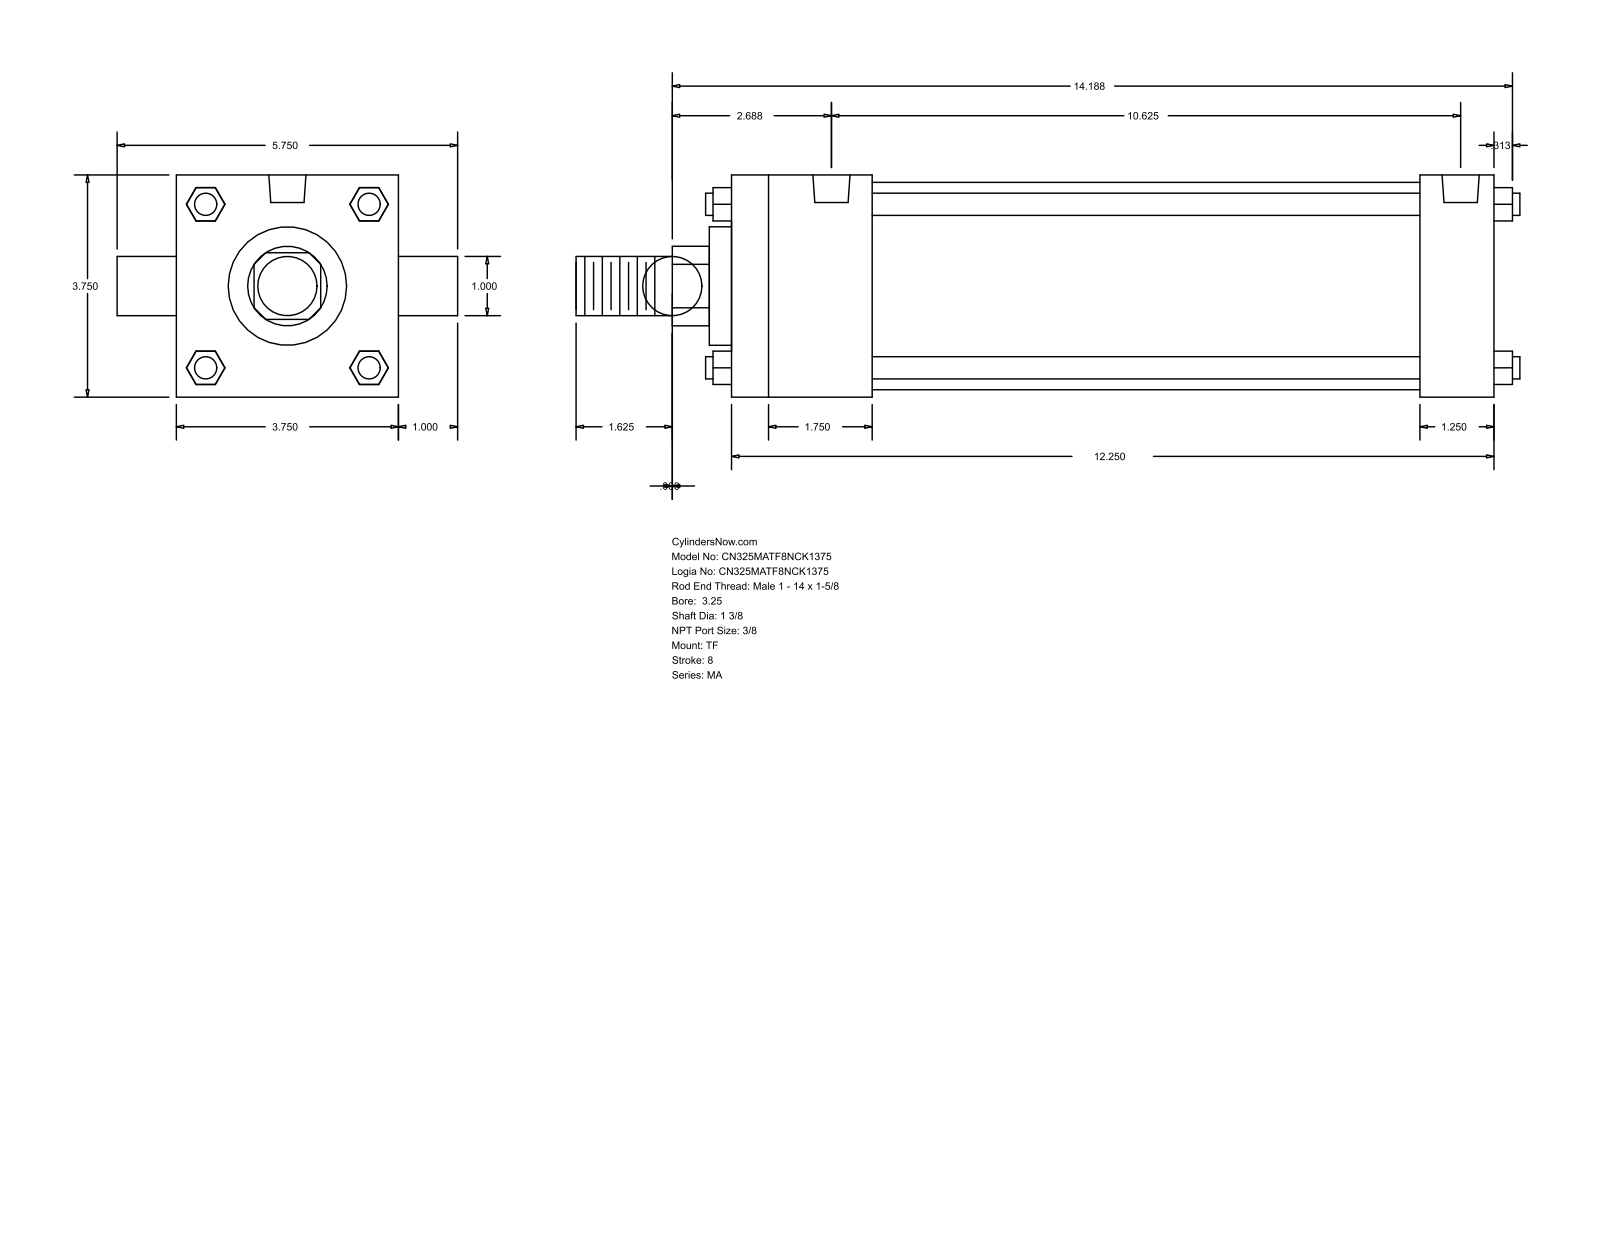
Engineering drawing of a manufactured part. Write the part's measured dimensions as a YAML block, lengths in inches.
part_name: "MA_TF__0325_1.375"
step_written_by: "GSSL Pune (CONFIG_CONTROL_DESIGN)"
units: inches
bodies: {solids: 0, faces: 120, planar: 92, cylindrical: 28, other: 0}
overall_size: [15.937, 5.75, 3.75]
round_holes:
  - {diameter: 0.437, count: 3}
  - {diameter: 0.627, count: 2}
round_bosses_or_shafts:
  - {diameter: 0.375, count: 4}
  - {diameter: 1, count: 2}
  - {diameter: 3.5, count: 1}
  - {diameter: 2, count: 1}
  - {diameter: 1.375, count: 1}
partial_cylinders:
  - {radius: 0.672, count: 1}
face_to_face_distances: [3.75, 12.875, 2.375, 11.625, 9.25, 10.5, 1.25, 0.375, 2.75, 12]
hole_center_spacings: [0.187, 0.188, 10.25, 10.437, 10.438, 10.625]
